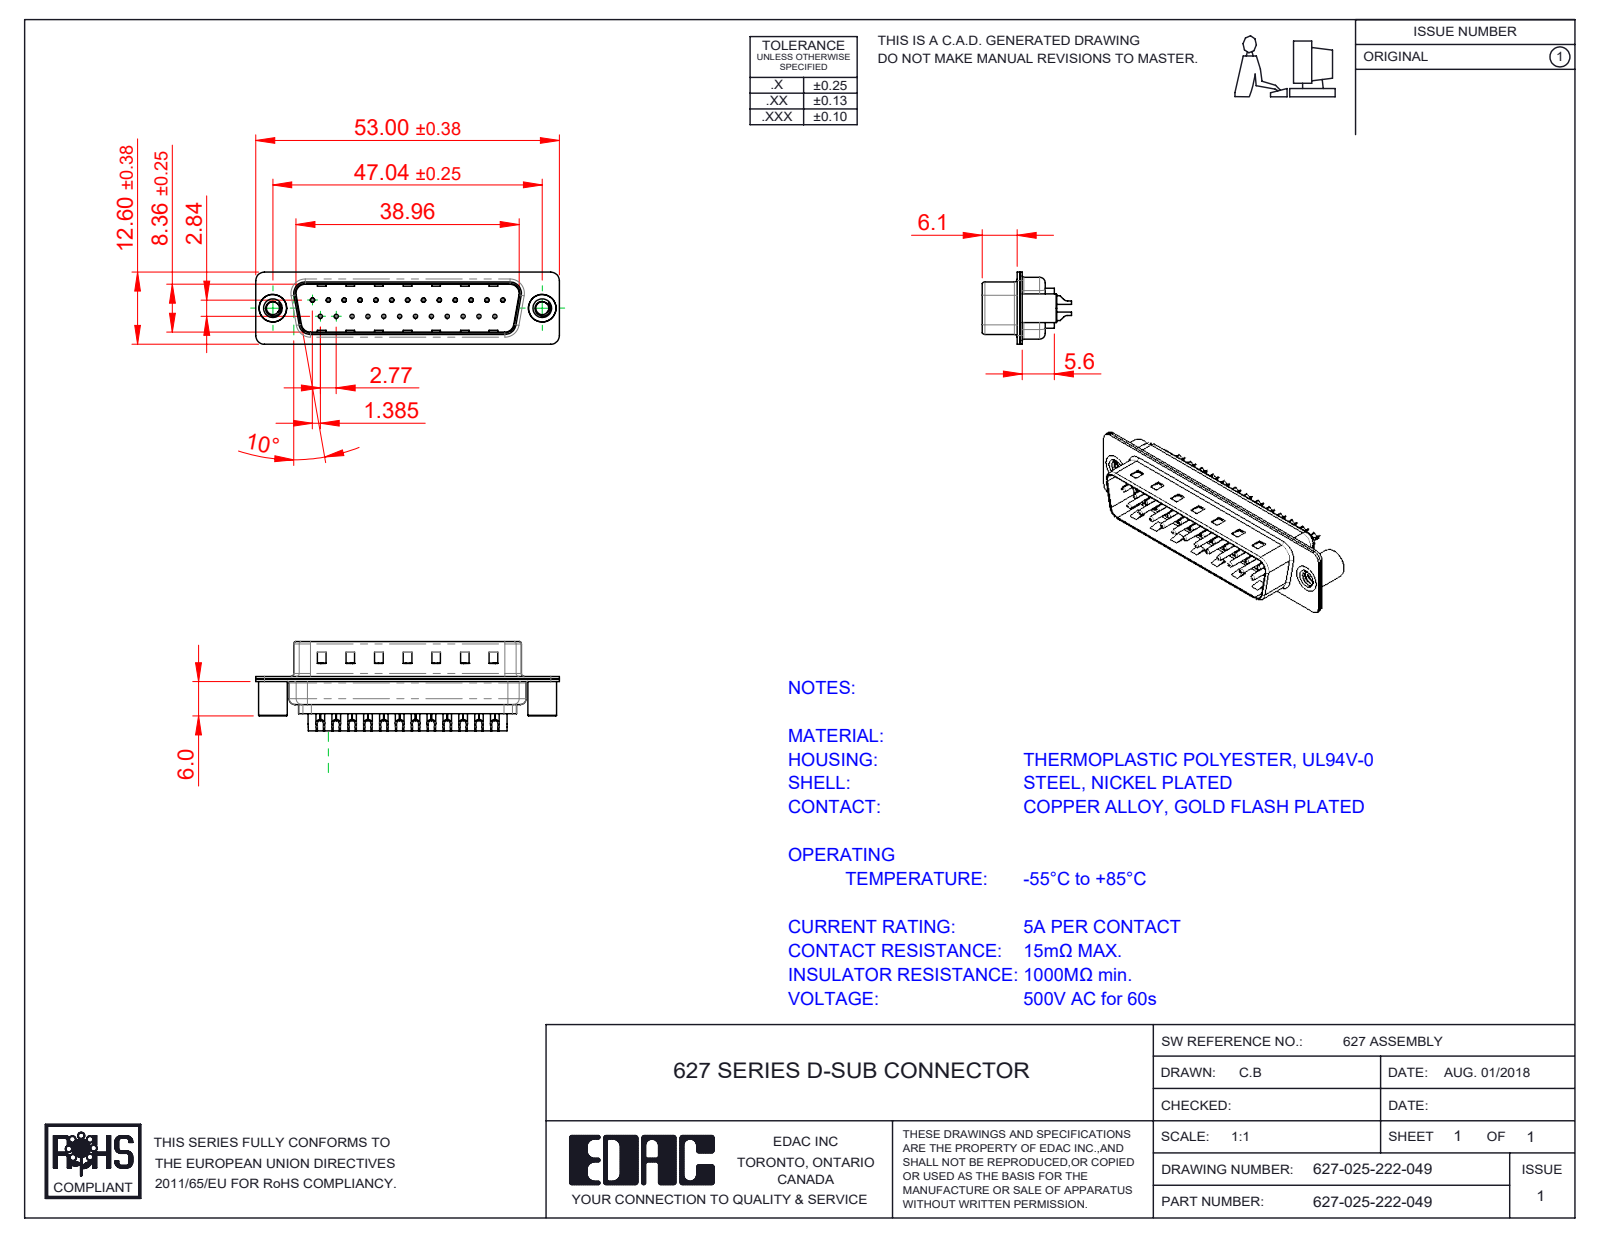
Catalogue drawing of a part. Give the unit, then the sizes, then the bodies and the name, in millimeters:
Units: millimetres
Overall size (bounding box): 53 × 15.35 × 12.6
Round holes (diameter × count): ⌀0.35 ×25, ⌀1.1 ×25, ⌀1.6 ×25, ⌀2.26 ×2, ⌀4 ×2, ⌀4.8 ×2
Round bosses / shafts (diameter × count): ⌀2 ×25, ⌀1.5 ×25, ⌀0.75 ×25, ⌀5 ×2, ⌀4.9 ×2
Partial cylindrical surfaces — rounded edges, fillets, slot ends (radius × count): R1.5 ×16, R2 ×12, R0.5 ×8, R1.6 ×8, R1 ×6, R0.25 ×4, R0.6 ×4, R0.65 ×4
Main face-to-face distances: 0.4, 0.45, 0.82, 9.58, 8.76, 0.9, 1.5, 6.5, 1.4, 6.05
Hole centre spacings: 3.16, 8.31, 2.77, 5.54, 11.08, 16.62, 5.03, 5.04
Volume: 2 787 mm³ · Surface area: 8 046 mm²
Bodies: 30 solids, 1998 faces (521 planar, 882 cylindrical, 595 other)
Part name (STEP PRODUCT): 627-025-222-049; 627 Contact Row 1_22L; 627 Housing_25 LP; 627 Contact Row 2_22L (+3 more)
STEP written by: SolidWorks 2020 (CONFIG_CONTROL_DESIGN)
